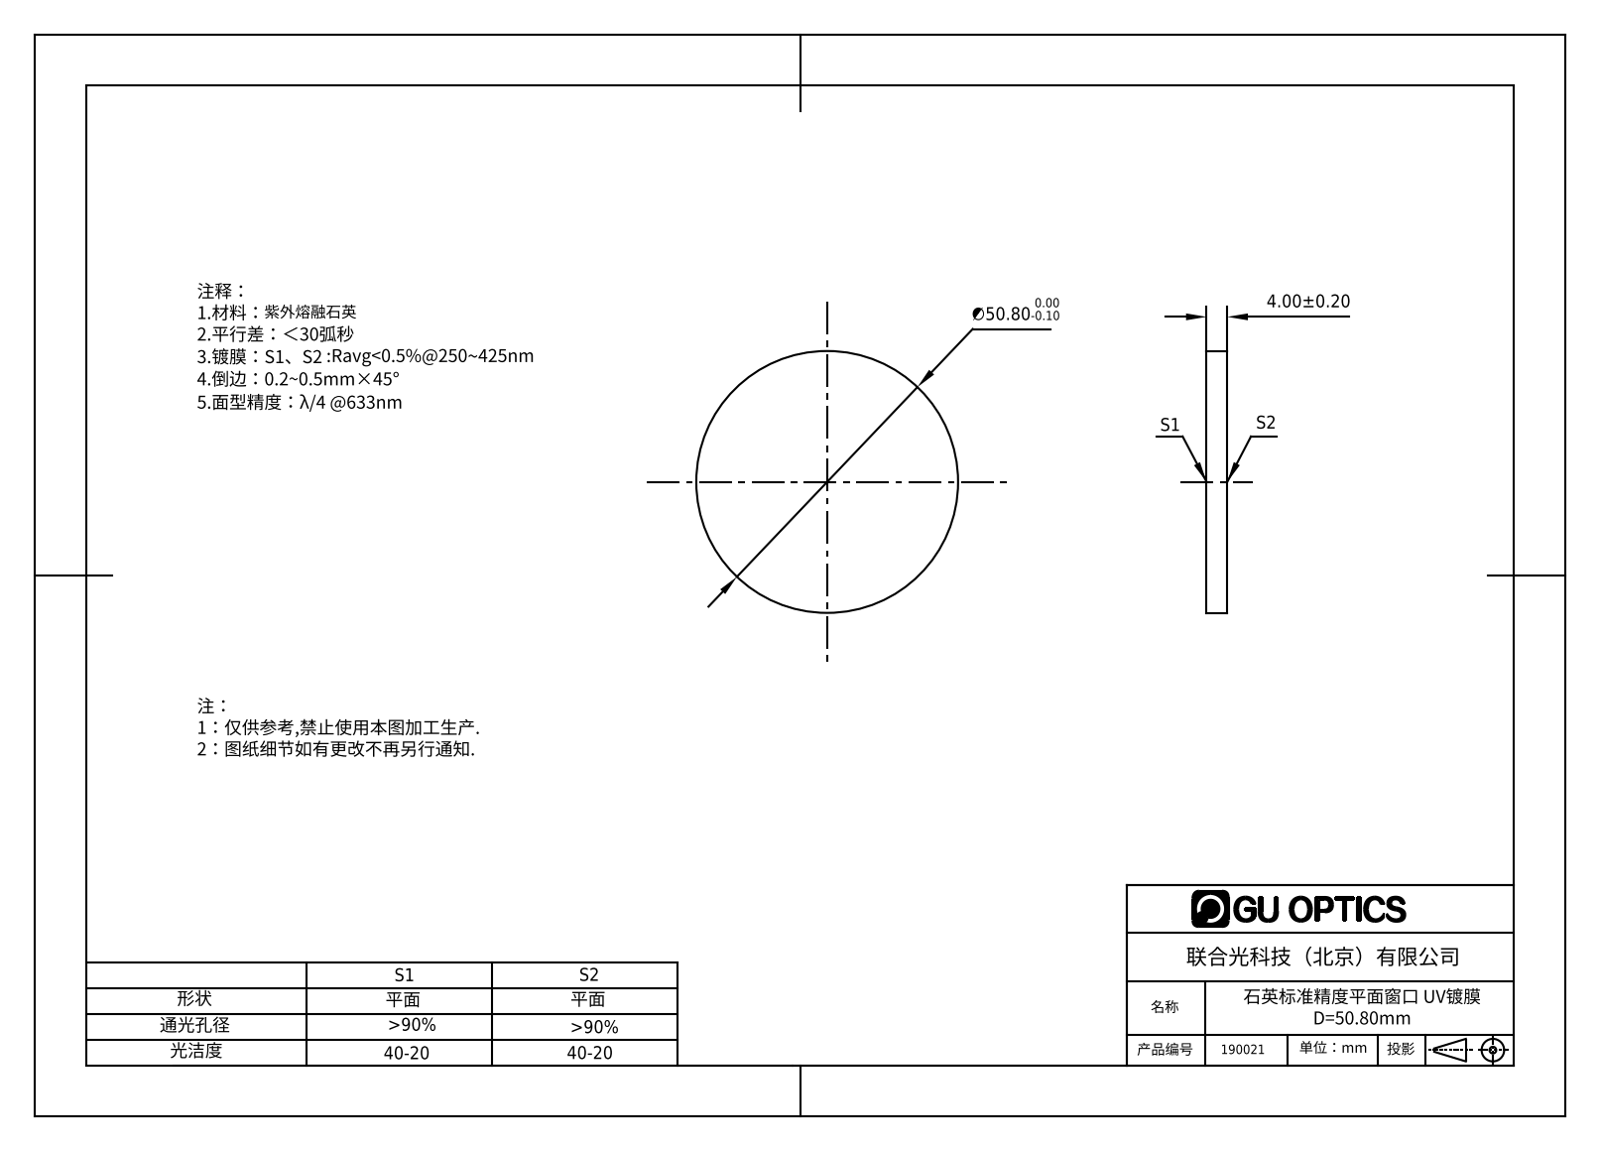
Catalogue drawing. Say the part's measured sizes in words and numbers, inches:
The part is named "180010". Its 3-D file was written by "SolidWorks 2016 (AUTOMOTIVE_DESIGN)". It is 1 solid with 4 faces: 2 planar, 2 cylindrical and 0 other. Overall it measures 2 by 2 by 0.157 inches. Its volume is 0.495 cubic inches and its surface area 7.273 square inches. Round bosses or shafts: 1 of diameter 2. The main face-to-face distances are 0.157.
